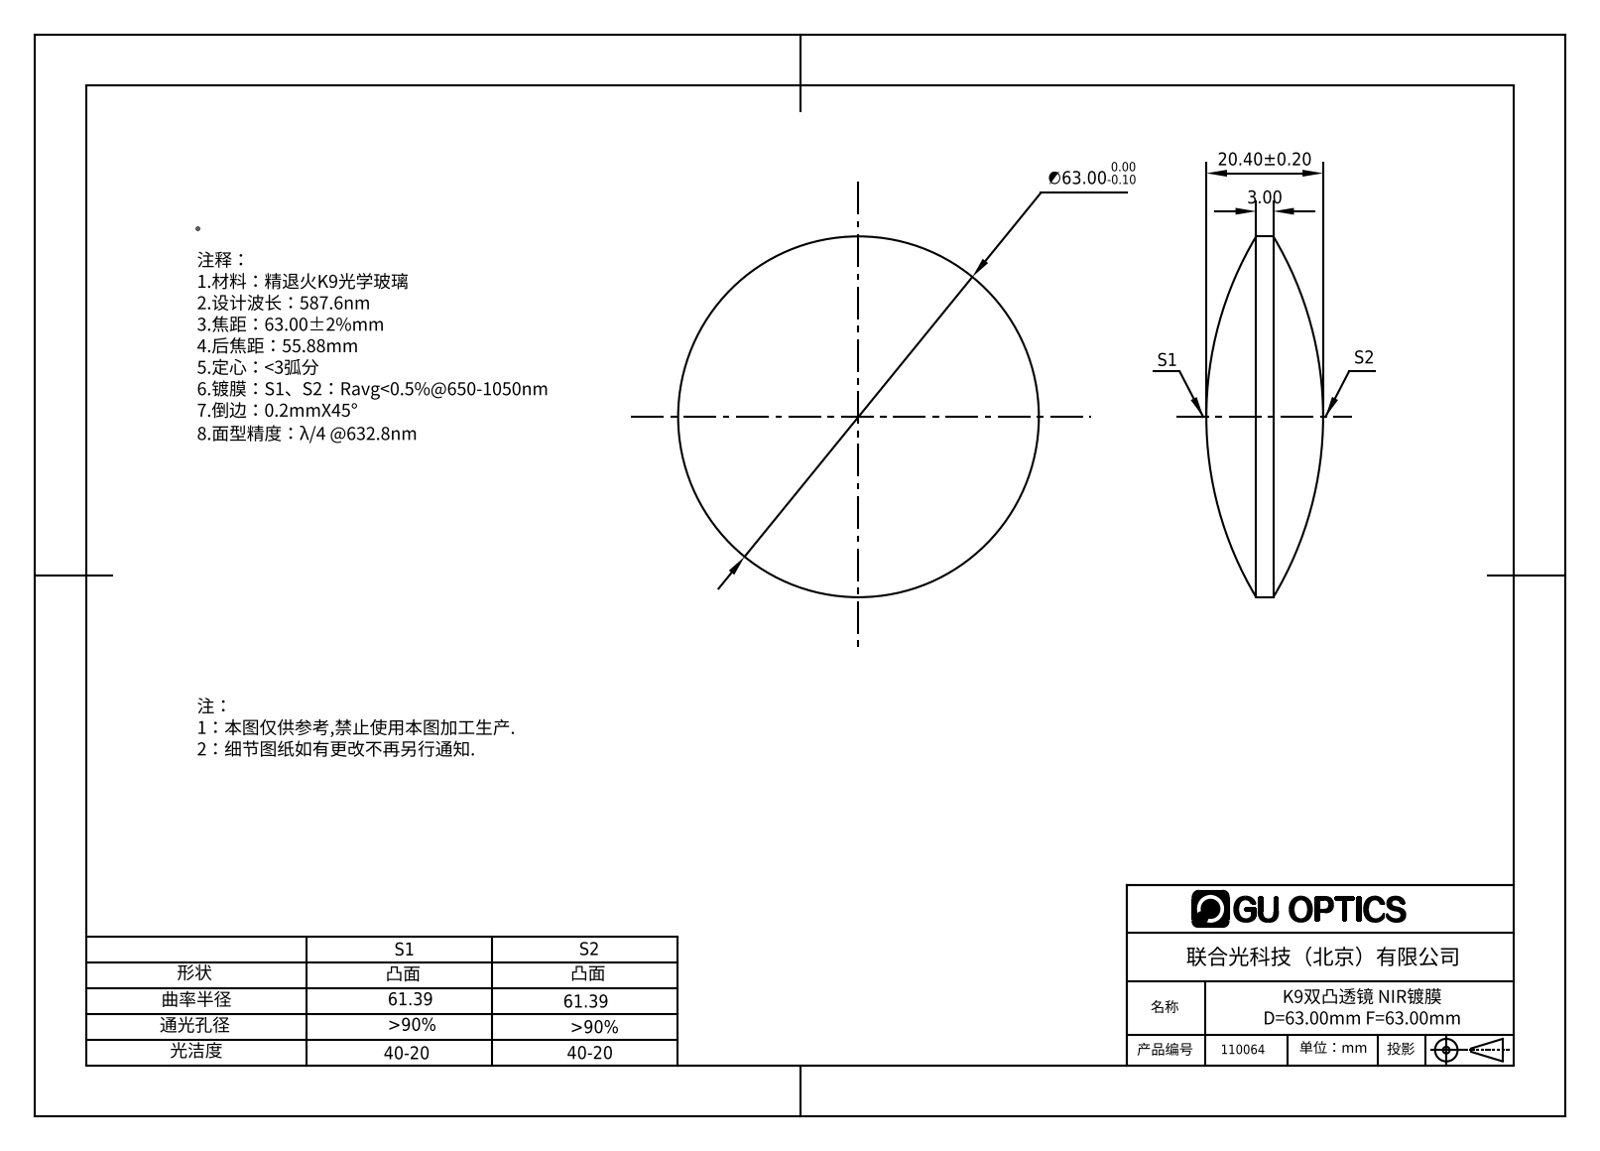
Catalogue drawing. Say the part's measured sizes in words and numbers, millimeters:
The part is named "110020". Its 3-D file was written by "SolidWorks 2016 (CONFIG_CONTROL_DESIGN)". It is 1 solid with 6 faces: 0 planar, 2 cylindrical and 4 other. Overall it measures 63 by 63 by 20.4 millimeters. Its volume is 37 158 cubic millimeters and its surface area 7 304 square millimeters. Round bosses or shafts: 1 of diameter 63.
